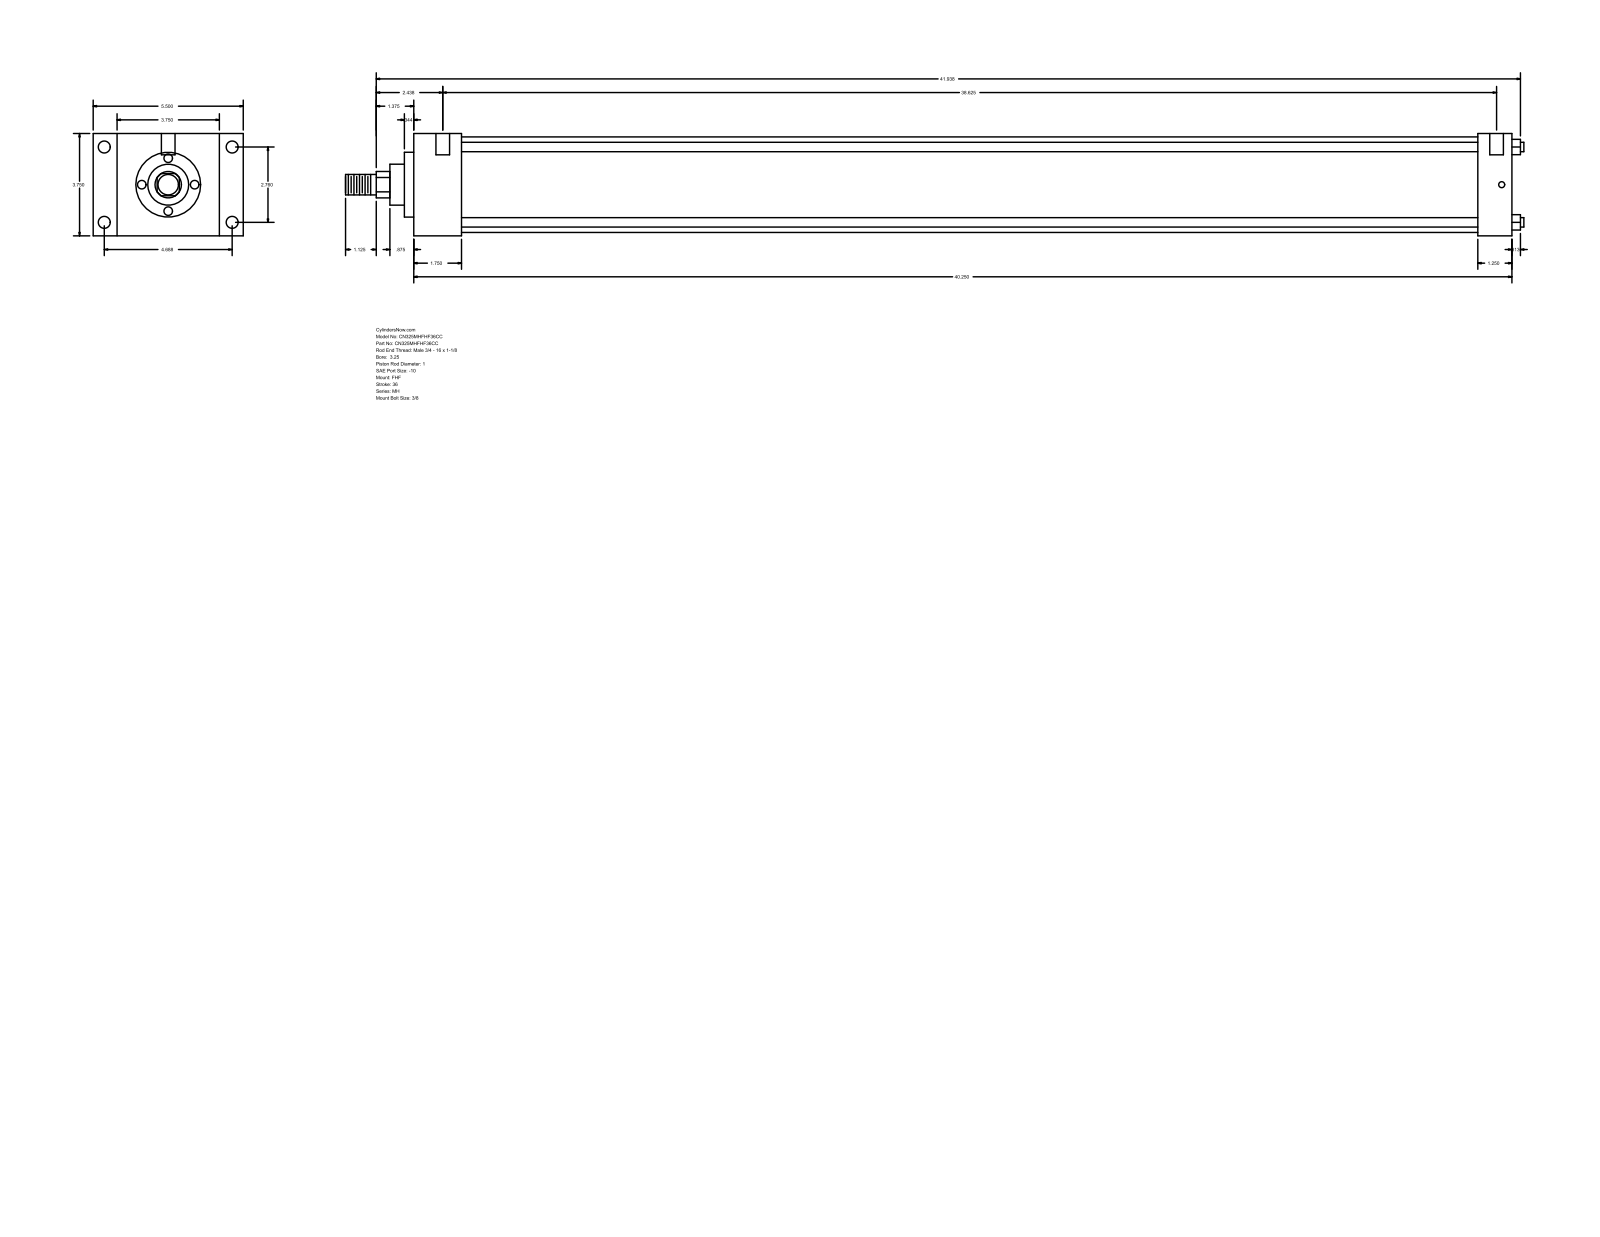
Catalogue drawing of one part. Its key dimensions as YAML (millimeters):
part_name: "MH_FHF__0325_1"
step_written_by: "GSSL Pune (CONFIG_CONTROL_DESIGN)"
units: millimeters
bodies: {solids: 0, faces: 90, planar: 61, cylindrical: 29, other: 0}
overall_size: [1096.96, 139.7, 95.25]
round_holes:
  - {diameter: 5.56, count: 4}
  - {diameter: 11.13, count: 4}
  - {diameter: 12.7, count: 2}
round_bosses_or_shafts:
  - {diameter: 8.76, count: 4}
  - {diameter: 88.9, count: 1}
  - {diameter: 60.33, count: 1}
  - {diameter: 38.1, count: 1}
  - {diameter: 25.4, count: 1}
  - {diameter: 19.05, count: 1}
partial_cylinders:
  - {radius: 12.29, count: 1}
face_to_face_distances: [95.24, 1022.36, 44.46, 977.9, 22.23, 117.47, 139.7, 990.61, 946.15, 31.75]
hole_center_spacings: [70.1, 119.06, 138.16, 987.42, 1.58, 4.76, 981.08, 982.66]
